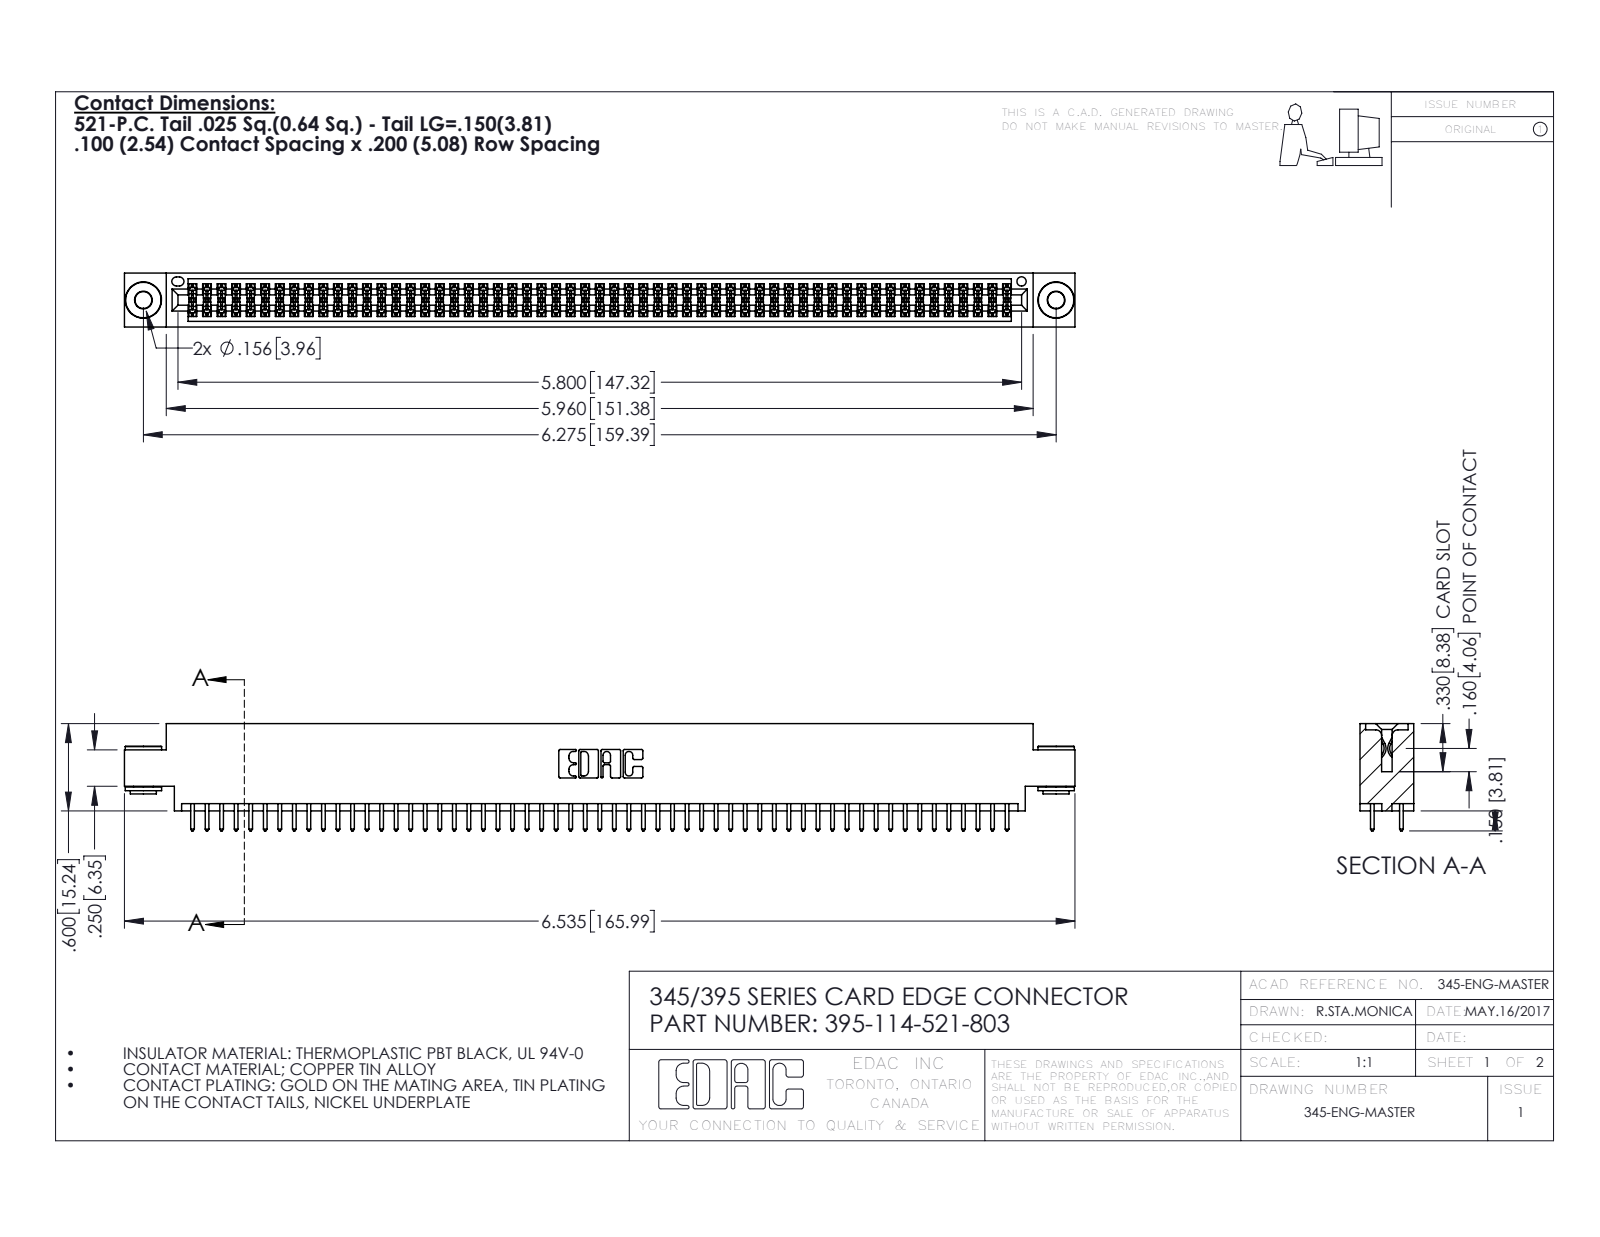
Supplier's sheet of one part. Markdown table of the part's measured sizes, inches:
| quantity | value |
| --- | --- |
| part name | 345-292-001_345-293-121; 345 Part_0.170 Offset - 0.156 Dia-TH; 395-114-521-803; 345-250-002_345-250-002-102 |
| STEP written by | SolidWorks 2016 (CONFIG_CONTROL_DESIGN) |
| units | inches |
| bodies | 117 solids, 5868 faces (3856 planar, 2004 cylindrical, 8 other) |
| overall size | 6.535 × 0.737 × 0.37 |
| volume | 0.984 in³ |
| surface area | 37.46 in² |
| round holes (diameter × count) | 0.116 × 2, 0.156 × 2, 0.064 × 1 |
| round bosses / shafts (diameter × count) | 0.25 × 2, 0.18 × 2, 0.136 × 2 |
| partial cylindrical surfaces (radius × count) | 0.006 × 171, 0.01 × 114, 0.01 × 22, 0.007 × 6, 0.031 × 6, 0.026 × 3, 0.014 × 2, 0.019 × 2 |
| main face-to-face distances | 0.072, 0.298, 0.37, 0.2, 0.098, 0.272, 0.025, 0.225, 0.175, 0.149 |
| hole center spacings | 0.27, 6.039, 6.275 |
